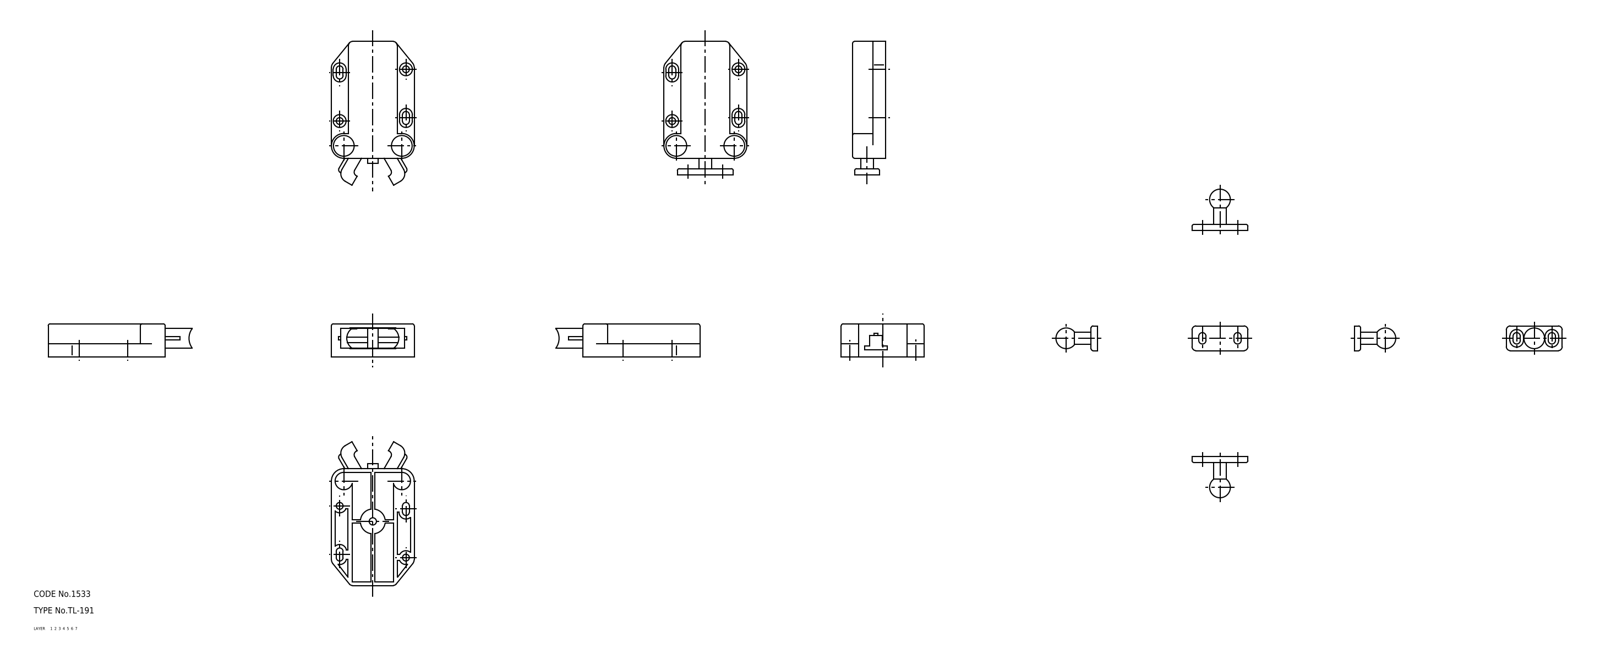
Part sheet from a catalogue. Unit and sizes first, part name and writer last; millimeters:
Units: millimetres
Overall size (bounding box): 106.5 × 40 × 16
Round holes (diameter × count): ⌀3.3 ×2, ⌀6.2 ×2, ⌀10 ×2, ⌀3.5 ×1
Round bosses / shafts (diameter × count): ⌀9.8 ×2, ⌀6.8 ×2, ⌀12 ×1, ⌀6 ×1
Partial cylindrical surfaces — rounded edges, fillets, slot ends (radius × count): R1 ×9, R2 ×8, R3.35 ×5, R1.65 ×4, R1.75 ×4, R3.1 ×4, R3.25 ×4, R1.5 ×2
Main face-to-face distances: 0.75, 1.75, 10.5, 3, 13, 11.25, 12.25, 3.75, 14.25, 16
Hole centre spacings: 24.01, 12.17, 17.67, 23.71, 28, 32.31, 37.05, 40.61
Volume: 17 641 mm³ · Surface area: 16 822 mm²
Bodies: 6 solids, 293 faces (171 planar, 104 cylindrical, 18 other)
Part name (STEP PRODUCT): housing; roller; TL_191; arm (+2 more)
STEP written by: SolidWorks 2015 (AUTOMOTIVE_DESIGN)
